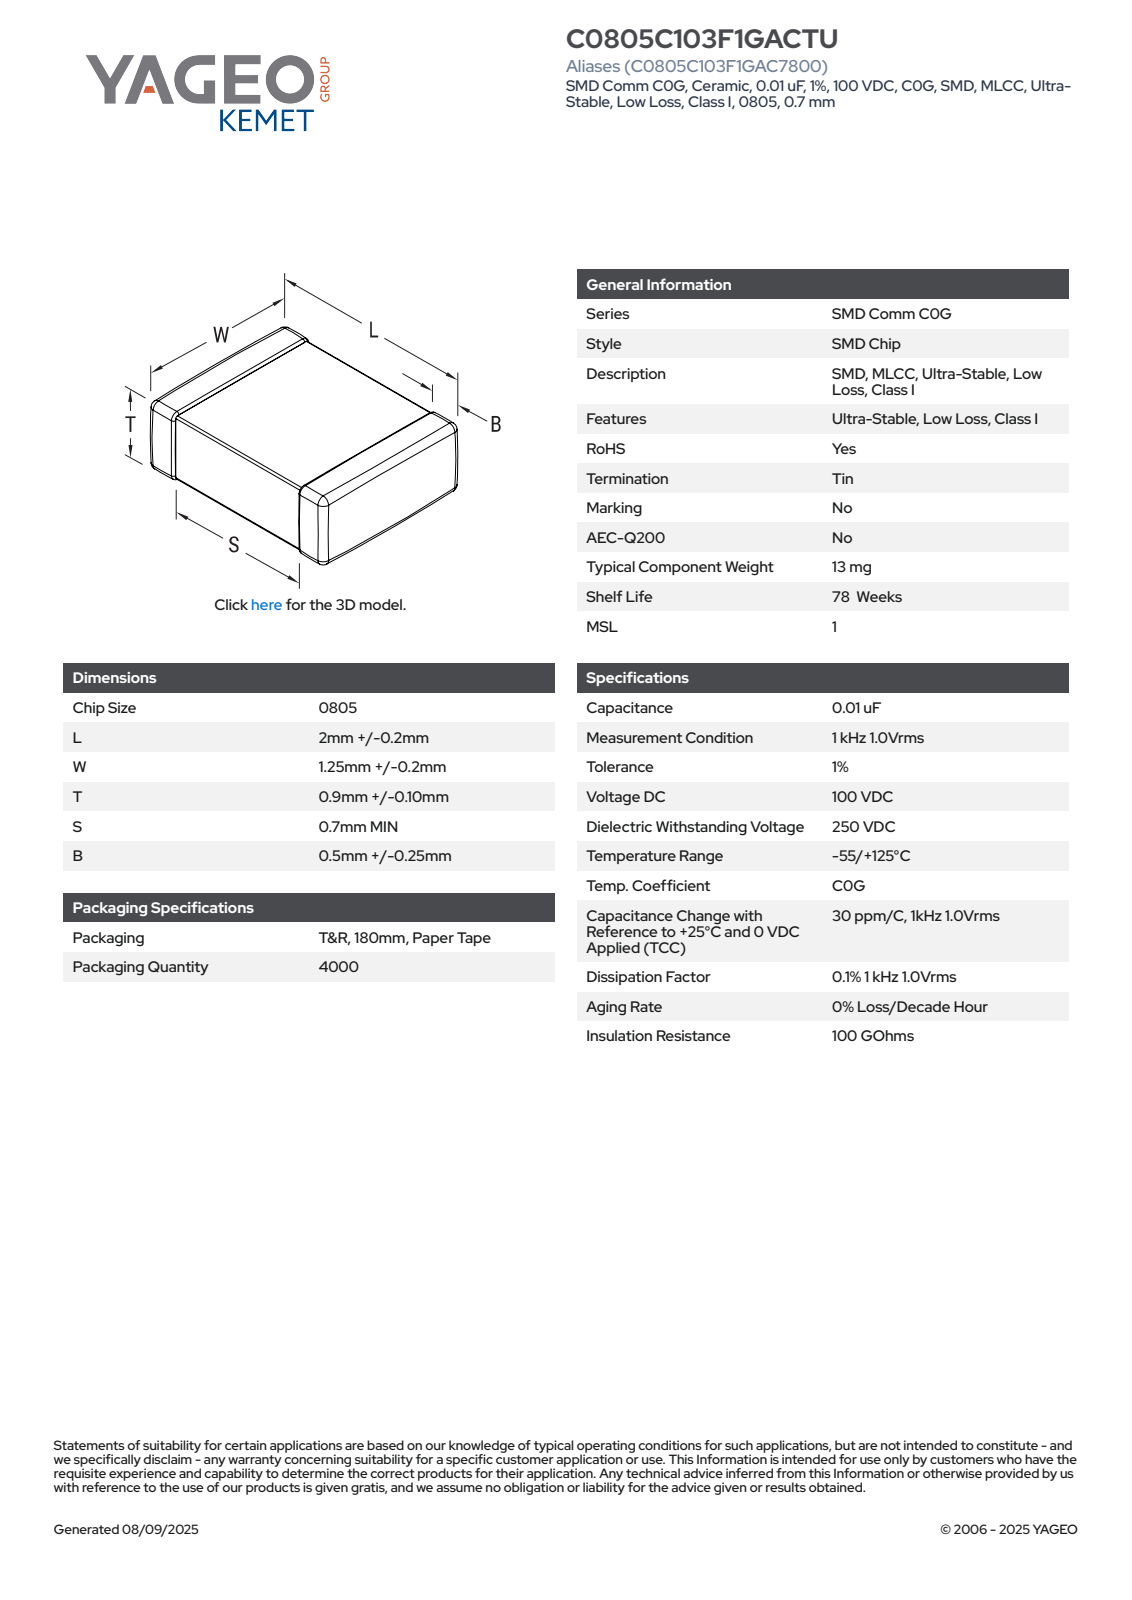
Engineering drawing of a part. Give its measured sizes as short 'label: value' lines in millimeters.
name: CCS_CCSTD_0805_L2.2W1.45T1B0.5
written by: SolidWorks 2014 (AUTOMOTIVE_DESIGN)
unit: mm
bodies: 4 solids, 125 faces (71 planar, 38 cylindrical, 16 other)
size: 2.2 × 1.45 × 1
volume: 3 mm³; area: 14 mm²
face distances: 0.97, 1.42, 0.94, 2.2, 1, 1.39, 1.45, 1.23, 1.19, 1.01
